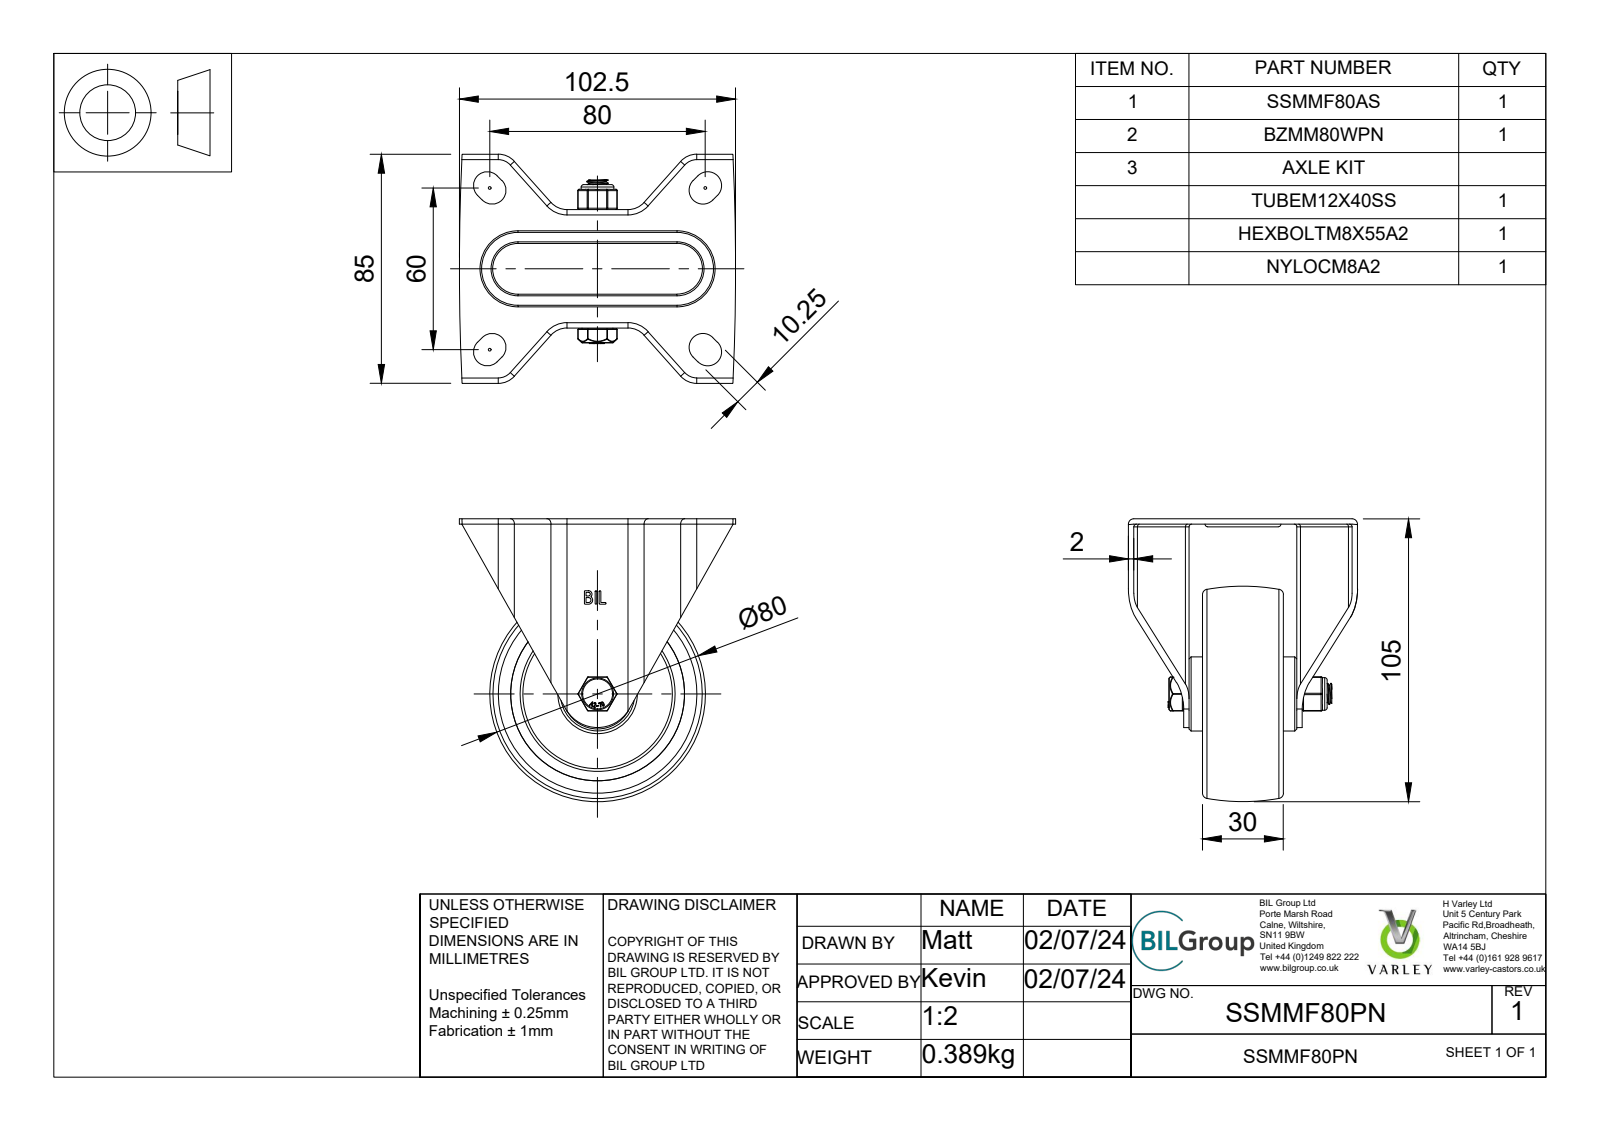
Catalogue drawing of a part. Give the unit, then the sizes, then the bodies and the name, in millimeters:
Units: millimetres
Overall size (bounding box): 105 × 102.5 × 85
Round holes (diameter × count): ⌀8 ×1, ⌀8.25 ×1, ⌀8.5 ×1, ⌀8.6 ×1, ⌀12.4 ×1, ⌀57.5 ×1, ⌀64.5 ×1
Round bosses / shafts (diameter × count): ⌀27.5 ×1, ⌀12.1 ×1, ⌀11.9 ×1, ⌀11.5 ×1, ⌀7.87 ×1, ⌀6.45 ×1
Partial cylindrical surfaces — rounded edges, fillets, slot ends (radius × count): R0.5 ×18, R0.25 ×12, R1 ×12, R2 ×8, R4 ×8, R5.12 ×8, R8 ×8, R0.6 ×4
Main face-to-face distances: 2, 5.16, 18.75, 21.25, 13.75, 20.75, 5, 35, 16.25, 23.25
Volume: 132 575 mm³ · Surface area: 78 293 mm²
Bodies: 7 solids, 400 faces (126 planar, 146 cylindrical, 128 other)
Part name (STEP PRODUCT): SSMMF80PN v3; SSMMF80AS - 40 v1; ZINC PLATED, PRESSED STEEL BRACKET; BZMM80WPN v1 (+8 more)
STEP written by: Autodesk Translation Framework v13.14.0.145 (AUTOMOTIVE_DESIGN)
